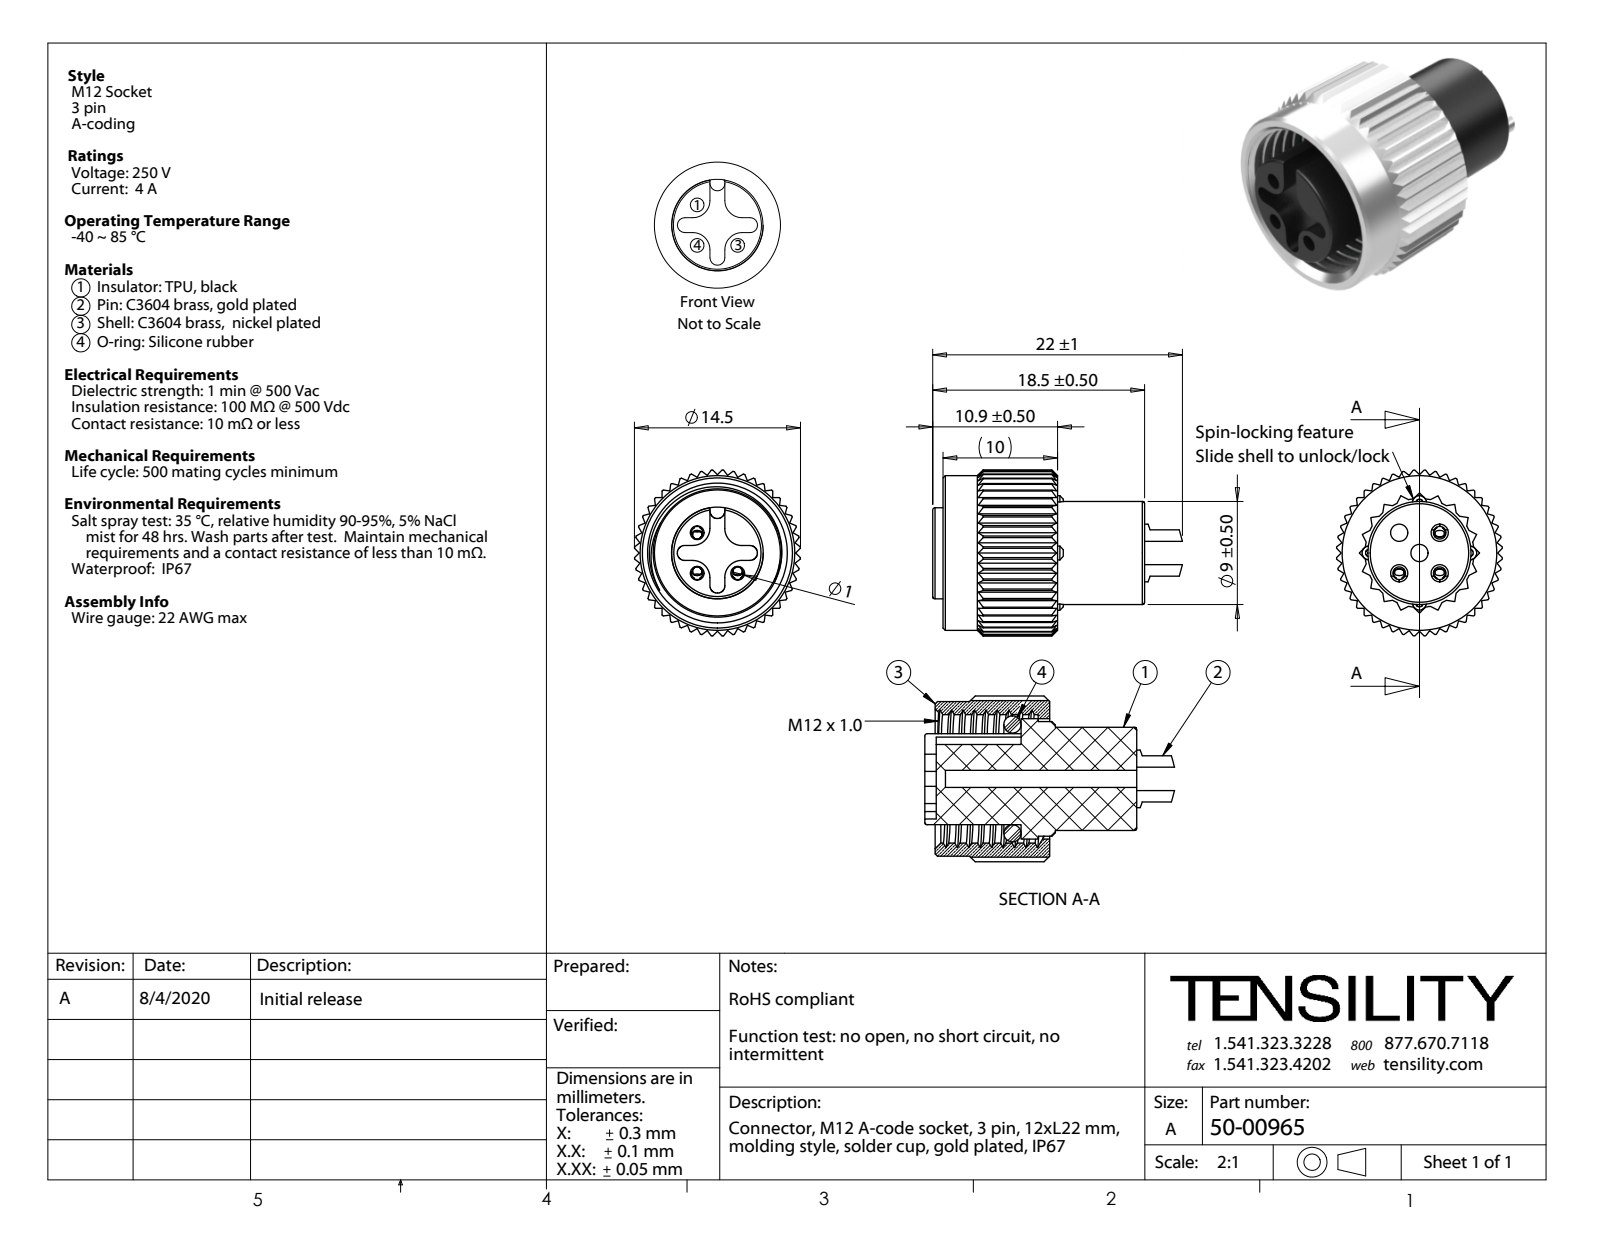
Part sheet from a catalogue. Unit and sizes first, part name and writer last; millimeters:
Units: millimetres
Overall size (bounding box): 21.8 × 14.48 × 14.48
Round holes (diameter × count): ⌀1.1 ×3, ⌀1.2 ×3, ⌀1.5 ×2, ⌀11.2 ×1
Round bosses / shafts (diameter × count): ⌀1.6 ×3, ⌀1.5 ×3, ⌀13.5 ×1, ⌀10.5 ×1, ⌀9 ×1, ⌀8 ×1
Partial cylindrical surfaces — rounded edges, fillets, slot ends (radius × count): R0.1 ×6, R0.4 ×5, R0.6 ×4, R0.65 ×4, R1.5 ×4, R4.75 ×1, R7.25 ×1
Main face-to-face distances: 9.66, 7.6, 1, 9.9, 2.5, 10.1, 1.5, 8.6, 8.4, 10.9
Hole centre spacings: 2.5, 3.54, 5.01
Volume: 1 538 mm³ · Surface area: 2 914 mm²
Bodies: 6 solids, 586 faces (243 planar, 201 cylindrical, 142 other)
Part name (STEP PRODUCT): 50-00965-04; 50-00965-02; 50-00965-03; 50-00965-01 (+1 more)
STEP written by: SolidWorks 2015 (CONFIG_CONTROL_DESIGN)
